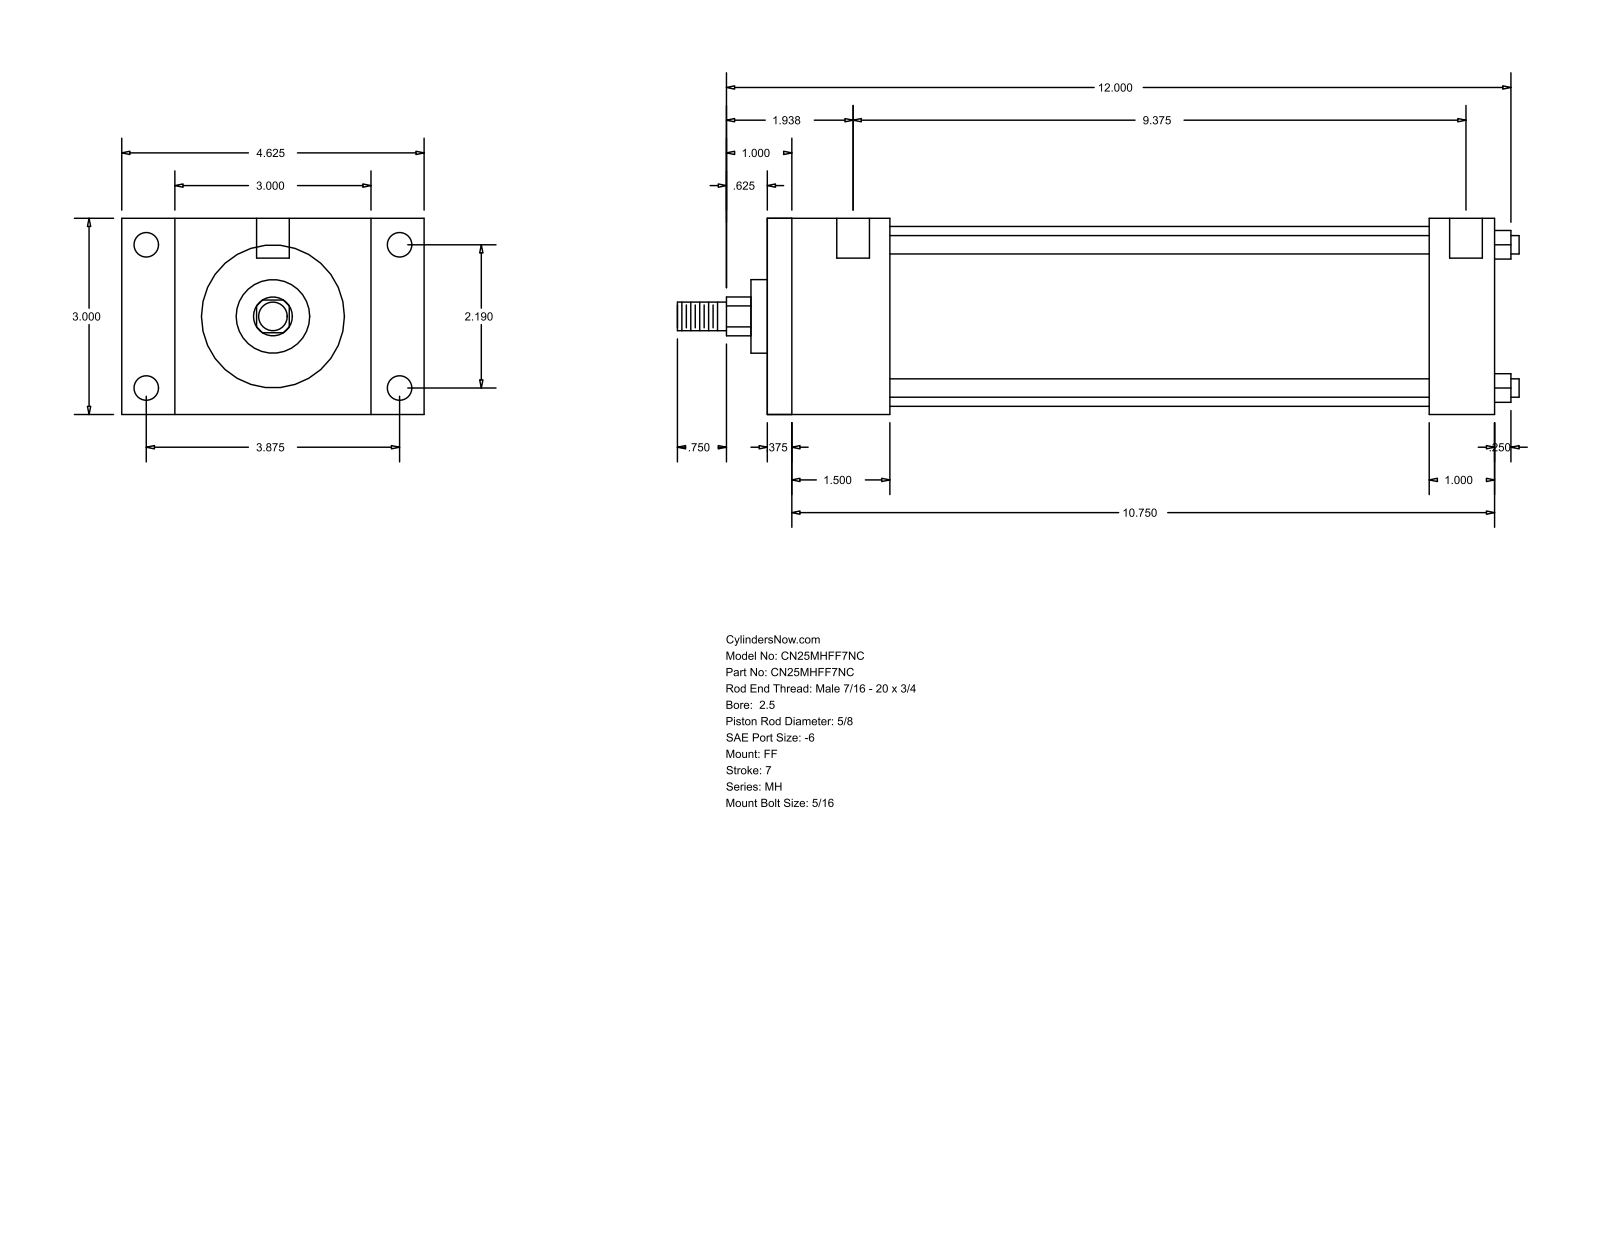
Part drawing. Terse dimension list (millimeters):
name: MH_FF__0250_0.625
written by: GSSL Pune (CONFIG_CONTROL_DESIGN)
unit: mm
bodies: 0 solids, 92 faces (64 planar, 28 cylindrical, 0 other)
size: 327.02 × 117.47 × 76.2
holes: 4× ⌀5.56, 4× ⌀9.53, 2× ⌀12.7
bosses: 4× ⌀7.14, 1× ⌀69.85, 1× ⌀28.57, 1× ⌀15.88, 1× ⌀11.11
rounds: 1× R7.54
face distances: 76.2, 282.57, 273.05, 9.52, 25.4, 47.62, 257.17, 38.1, 247.65, 209.55
hole spacings: 55.62, 98.42, 113.05, 246.06, 3.17, 4.76, 238.13, 241.3
